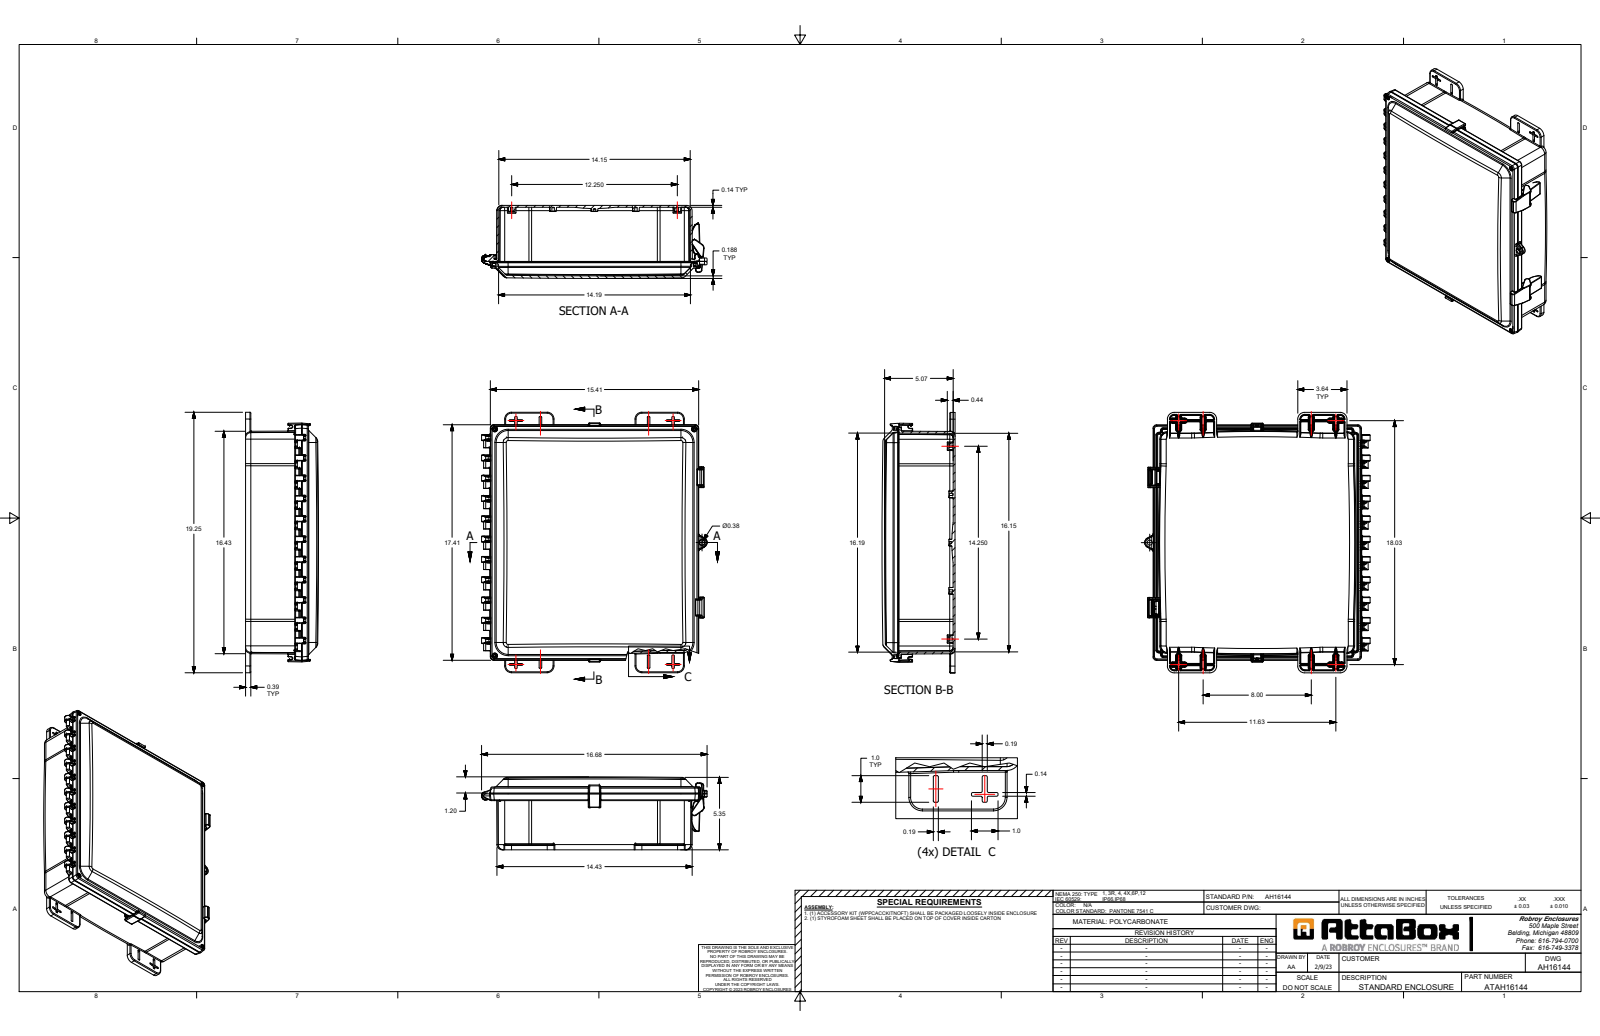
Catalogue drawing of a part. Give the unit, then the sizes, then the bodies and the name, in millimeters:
Units: millimetres
Overall size (bounding box): 489 × 423.6 × 137.1
Round holes (diameter × count): ⌀4.7 ×21, ⌀5 ×4, ⌀6.4 ×4, ⌀7.5 ×4, ⌀9.9 ×4, ⌀8.3 ×1, ⌀9.5 ×1, ⌀11.4 ×1
Round bosses / shafts (diameter × count): ⌀12.4 ×21, ⌀15.9 ×4, ⌀5.1 ×3, ⌀8 ×1
Partial cylindrical surfaces — rounded edges, fillets, slot ends (radius × count): R0.9 ×211, R1.7 ×36, R0.3 ×24, R1.3 ×16, R12.7 ×8, R130.6 ×8, R0.6 ×6, R2.3 ×4
Main face-to-face distances: 3.6, 361.9, 12.7, 12.7, 4.7, 101.6, 412.6, 105.2, 92.5, 88.9
Hole centre spacings: 119.3, 180, 197, 238.7, 250.3, 295.3, 312.9, 77.8
Volume: 2 433 000 mm³ · Surface area: 1 160 000 mm²
Bodies: 6 solids, 1520 faces (551 planar, 510 cylindrical, 459 other)
Part name (STEP PRODUCT): AH16144C
STEP written by: SolidWorks 2023 (AUTOMOTIVE_DESIGN)
